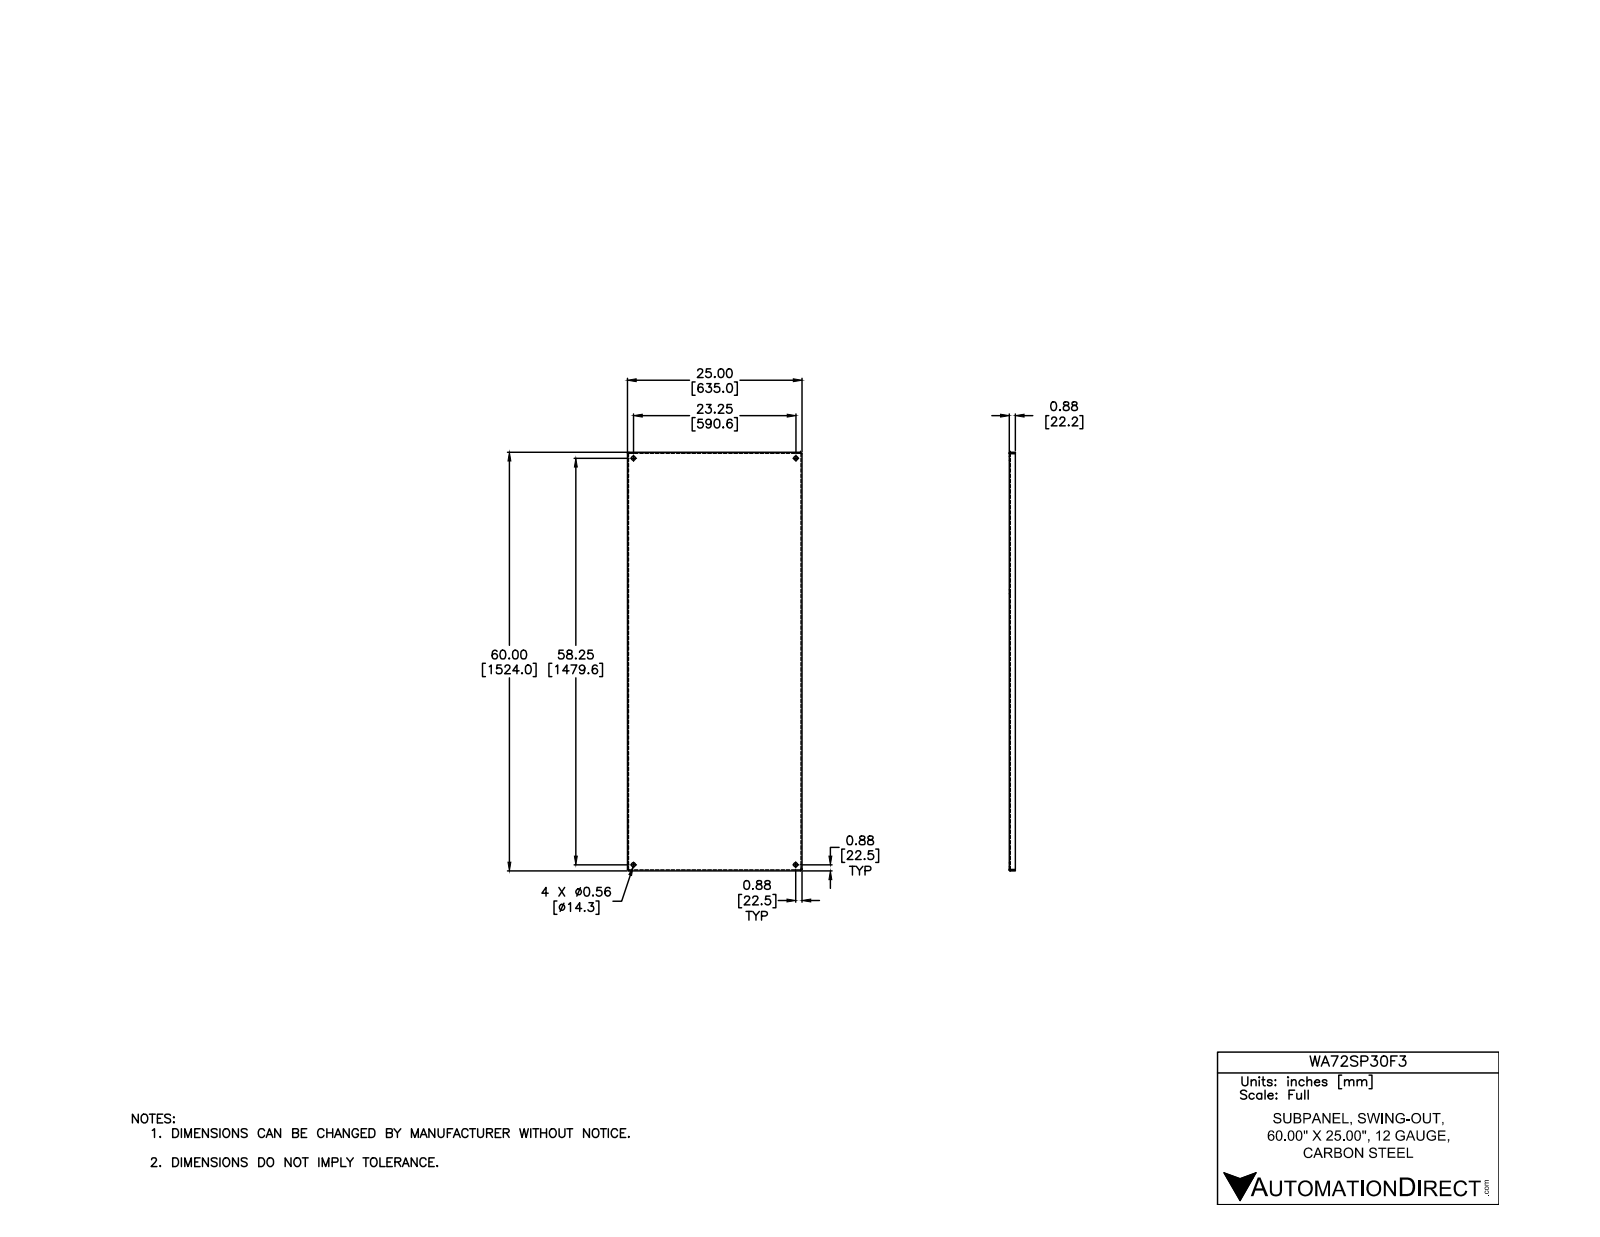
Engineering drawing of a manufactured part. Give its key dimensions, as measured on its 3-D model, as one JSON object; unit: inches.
{"part_name": "WA60SP24F3-WA90SP36F4", "step_written_by": "Autodesk Inventor 2012 (AUTOMOTIVE_DESIGN)", "units": "inches", "bodies": {"solids": 1, "faces": 42, "planar": 22, "cylindrical": 12, "other": 8}, "overall_size": [60, 25, 0.875], "volume_in3": 152.4, "surface_area_in2": 3267, "round_holes": [[0.563, 4]], "partial_cylinders_radius": [[0.031, 4], [0.125, 4]], "face_to_face_distances": [0.094, 24.906, 25, 24.813, 59.906, 60, 59.813, 0.781, 0.875, 0.16], "hole_center_spacings": [23.25, 58.25, 62.719]}
